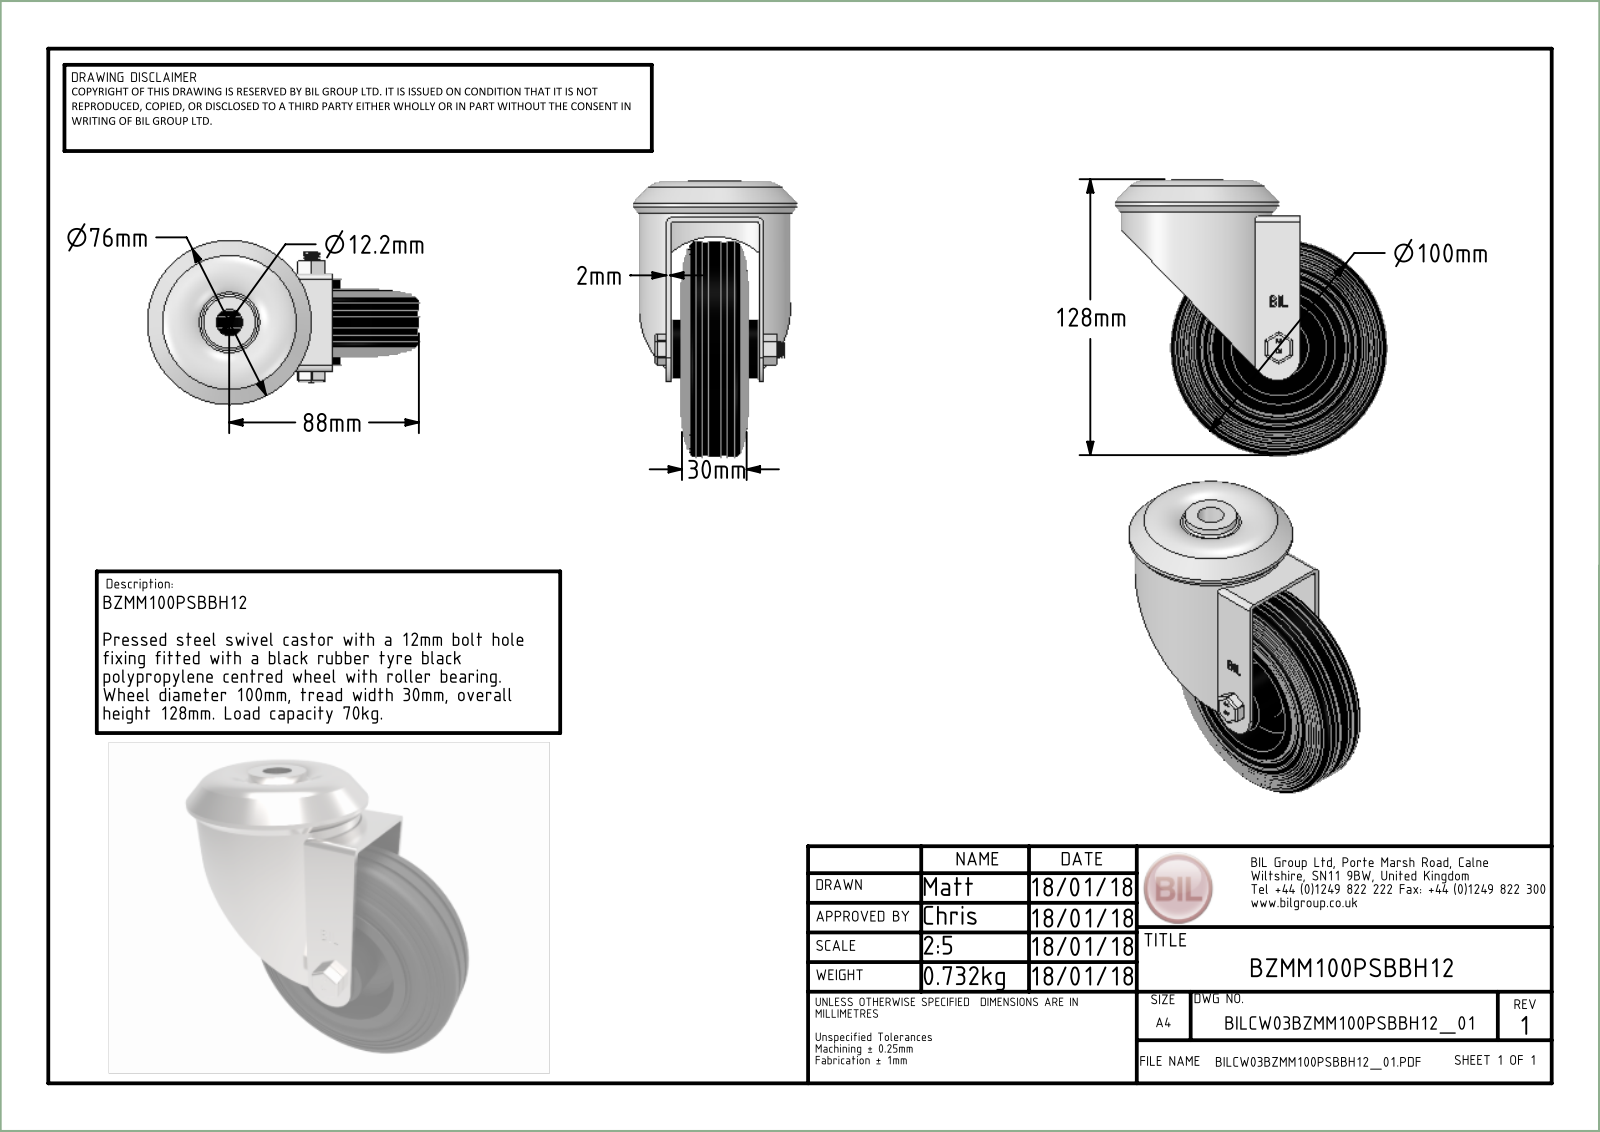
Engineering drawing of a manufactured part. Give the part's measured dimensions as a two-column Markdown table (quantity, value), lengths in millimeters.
| quantity | value |
| --- | --- |
| part name | BZMM100ASBH12; ZINC PLATED PRESSED STEEL HEAD; ZINC PLATED, PRESSED STEEL FORKS; BZMM100PSBBH12 (+7 more) |
| STEP written by | Spatial InterOp 3D (AUTOMOTIVE_DESIGN) |
| units | millimeters |
| bodies | 18 solids, 714 faces (185 planar, 251 cylindrical, 278 other) |
| overall size | 128 × 126 × 76 |
| volume | 246 353 mm³ |
| surface area | 103 550 mm² |
| round holes (diameter × count) | 0.66 × 2, 8 × 1, 8.2 × 1, 8.4 × 1, 8.6 × 1, 12 × 1, 12.2 × 1, 13 × 1, 22 × 1, 25 × 1, 50.79 × 1, 65 × 1 |
| round bosses / shafts (diameter × count) | 4.5 × 8, 100 × 1, 99 × 1, 70 × 1, 61.5 × 1, 49.5 × 1, 38 × 1, 28 × 1 |
| partial cylindrical surfaces (radius × count) | 0.5 × 18, 0.25 × 12, 0.33 × 4, 0.64 × 4, 1.25 × 4, 0.63 × 2, 0.64 × 2, 2.5 × 2 |
| main face-to-face distances | 2.5, 18.75, 42.5, 3, 7.5, 16.25, 26.25, 23.75, 40, 32.63 |
| hole center spacings | 2.49, 3.21, 3.22 |
